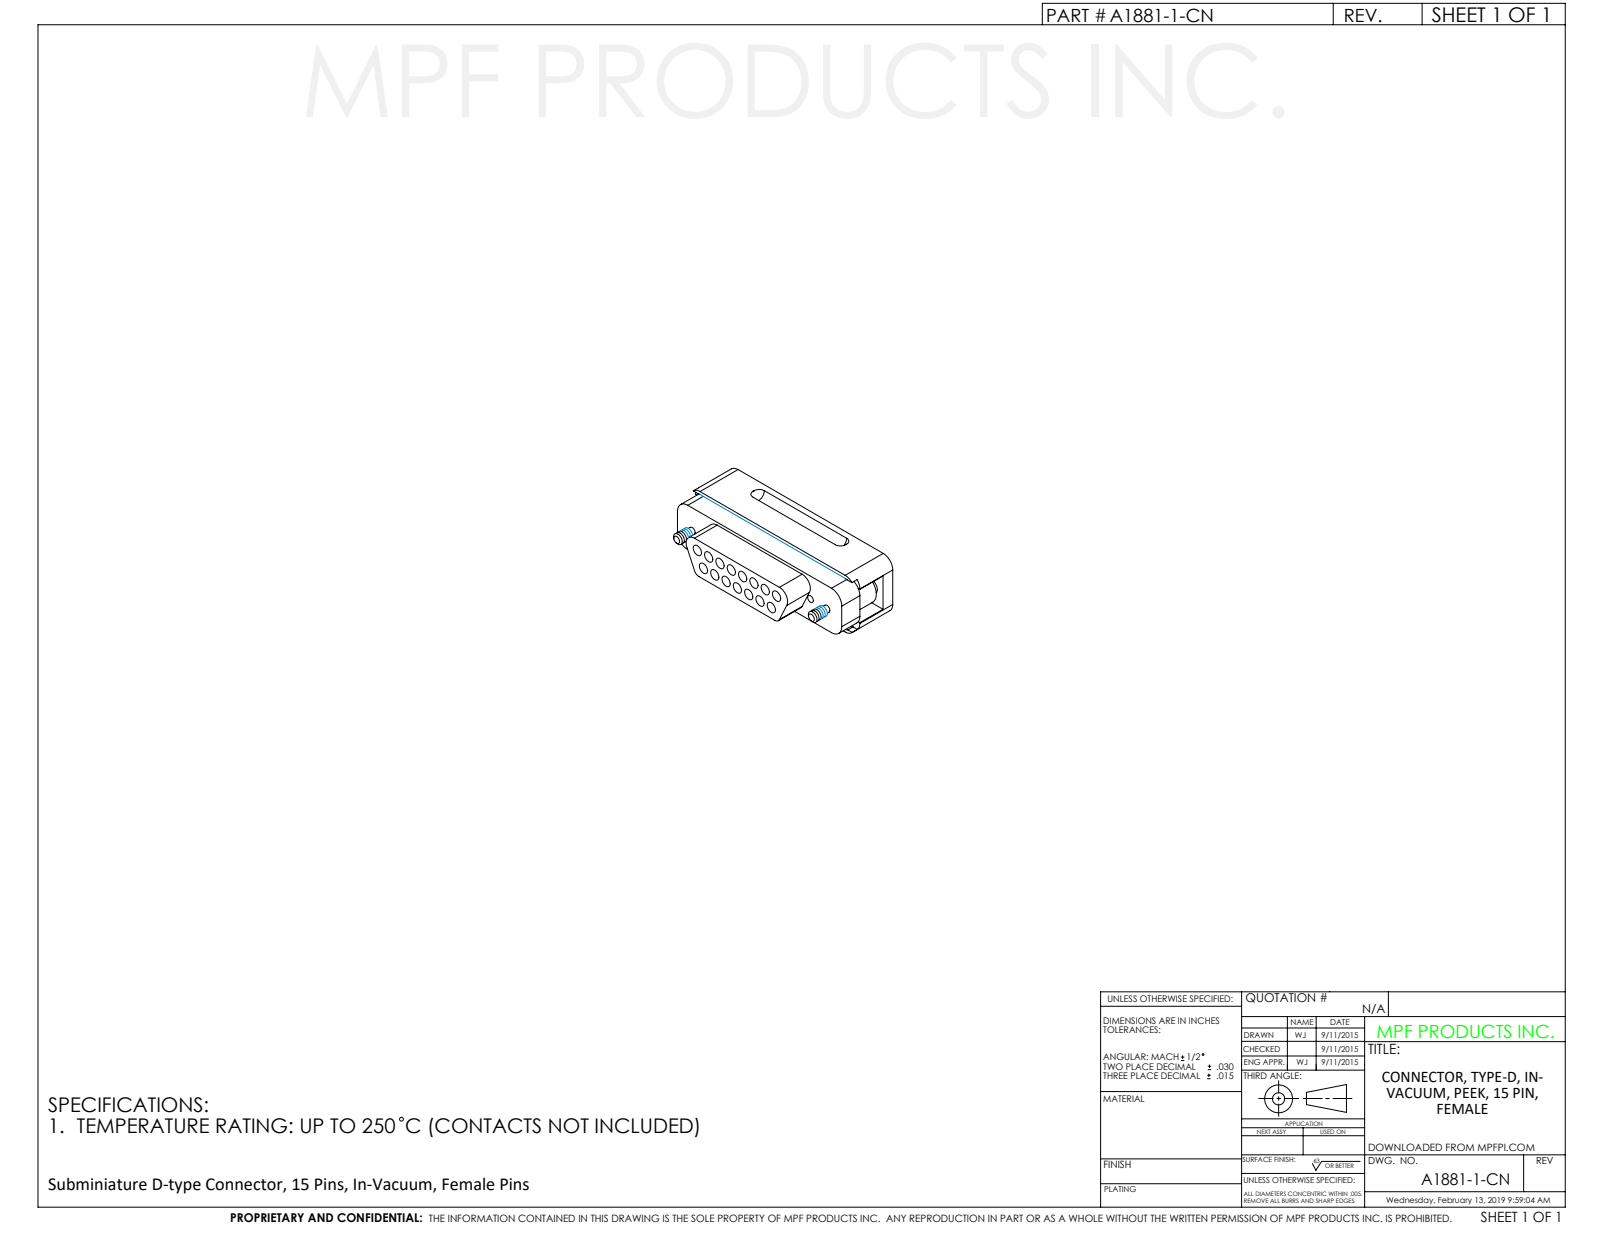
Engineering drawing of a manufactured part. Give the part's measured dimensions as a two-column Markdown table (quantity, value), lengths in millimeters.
| quantity | value |
| --- | --- |
| part name | A1881-1-CN |
| STEP written by | SolidWorks 2012 (CONFIG_CONTROL_DESIGN) |
| units | millimeters |
| bodies | 0 solids, 162 faces (47 planar, 73 cylindrical, 42 other) |
| overall size | 40.6 × 18.2 × 12.1 |
| round holes (diameter × count) | 2 × 15, 2.8 × 2, 3.8 × 2, 1.3 × 1, 1.4 × 1 |
| round bosses / shafts (diameter × count) | 6 × 2, 3.5 × 2, 1.4 × 2 |
| partial cylindrical surfaces (radius × count) | 1.7 × 4, 2.4 × 4, 2.5 × 4, 1.3 × 2, 1.4 × 2, 2 × 2 |
| main face-to-face distances | 12.1, 12.6, 10.8, 1.2, 1.4, 9.5, 10.7, 8.1, 4.5, 18.2 |
| hole center spacings | 5.6, 2.8, 3.4, 3.3, 8.4, 2.8, 5.1, 11.2 |
